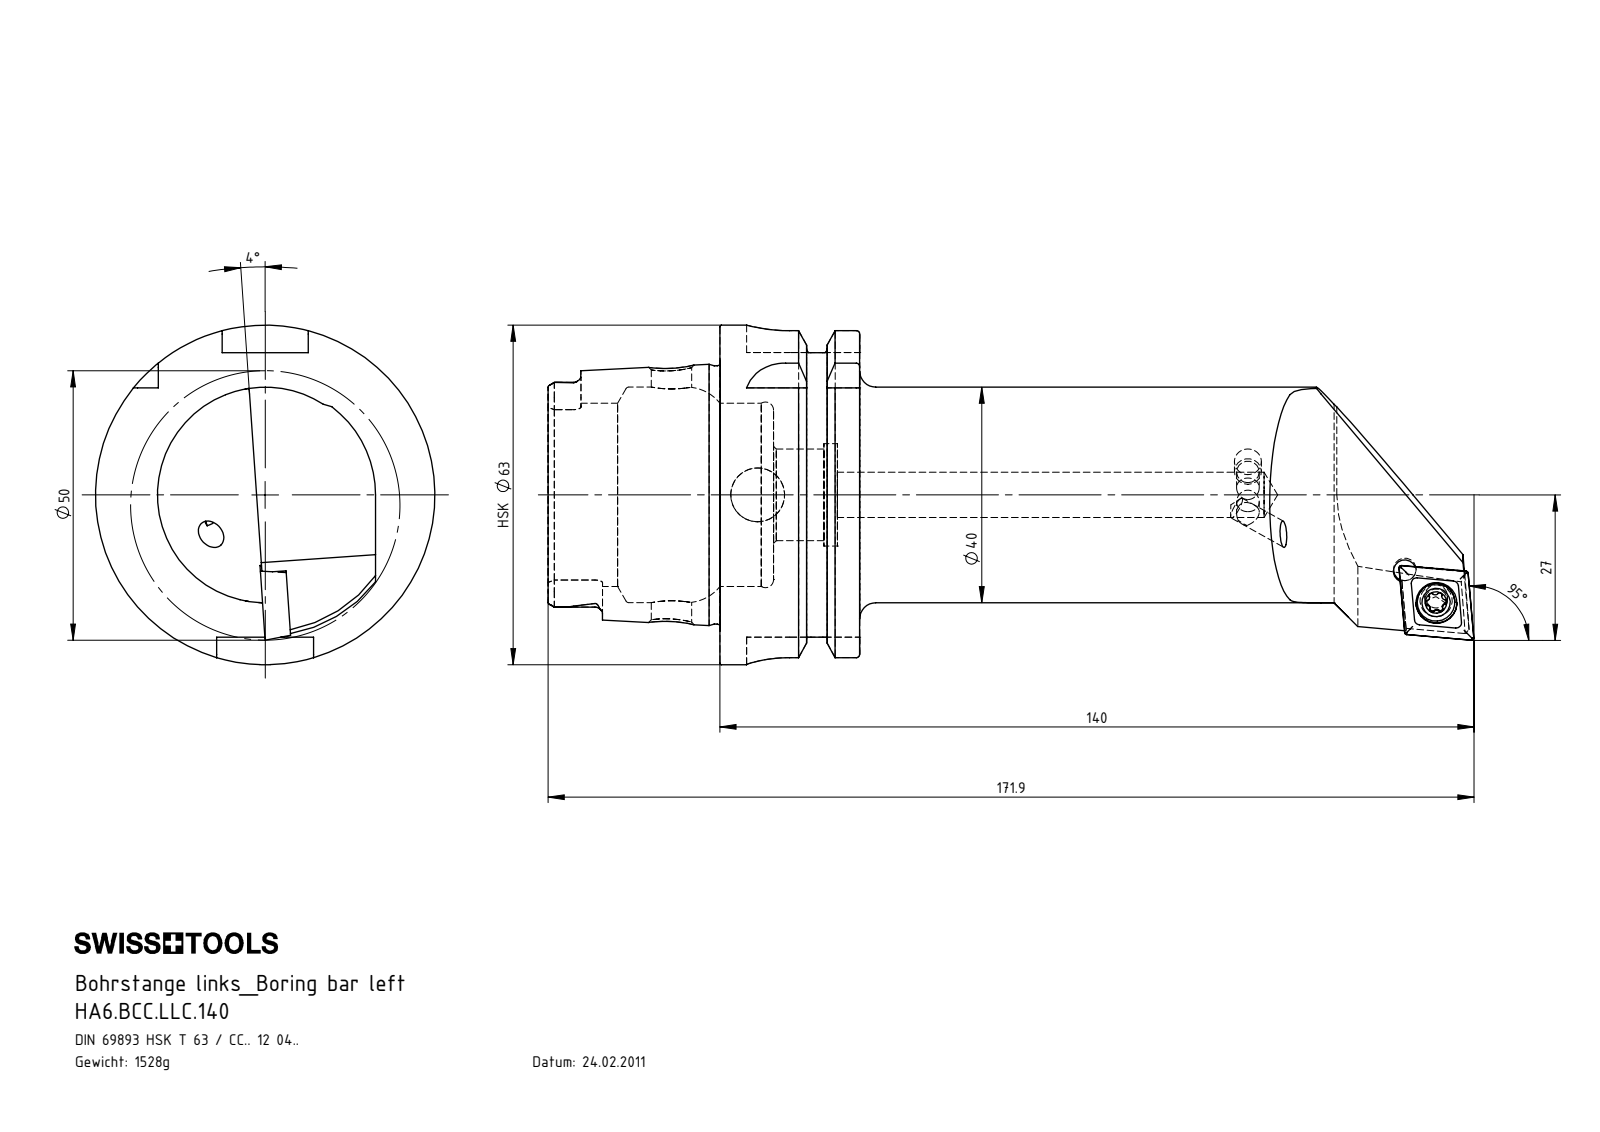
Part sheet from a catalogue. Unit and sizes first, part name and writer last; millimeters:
Units: millimetres
Overall size (bounding box): 171.86 × 63 × 63
Round holes (diameter × count): ⌀4.2 ×4, ⌀4 ×1, ⌀5.5 ×1, ⌀7.5 ×1, ⌀7.6 ×1, ⌀8.4 ×1, ⌀10 ×1, ⌀17 ×1, ⌀19 ×1, ⌀34 ×1, ⌀40 ×1
Round bosses / shafts (diameter × count): ⌀5 ×2, ⌀63 ×1, ⌀54.95 ×1, ⌀47.94 ×1, ⌀7 ×1
Partial cylindrical surfaces — rounded edges, fillets, slot ends (radius × count): R0.39 ×6, R1.4 ×6, R8 ×4, R0.69 ×3, R0.69 ×3, R2.82 ×2, R2.88 ×2, R3 ×1
Main face-to-face distances: 25.95, 16, 9.95, 31.9, 41.85, 57.85, 52.8, 21.8, 11.85, 53.7
Hole centre spacings: 8.16, 8.32
Volume: 197 314 mm³ · Surface area: 38 724 mm²
Bodies: 5 solids, 297 faces (71 planar, 89 cylindrical, 137 other)
Part name (STEP PRODUCT): HA6.BCC.LLC.140; WCC-ER2.001.010_A; HA6-BCC.LLC.140_A; KVT_MB_600_050 (+1 more)
STEP written by: SolidWorks 2017 (AUTOMOTIVE_DESIGN)
